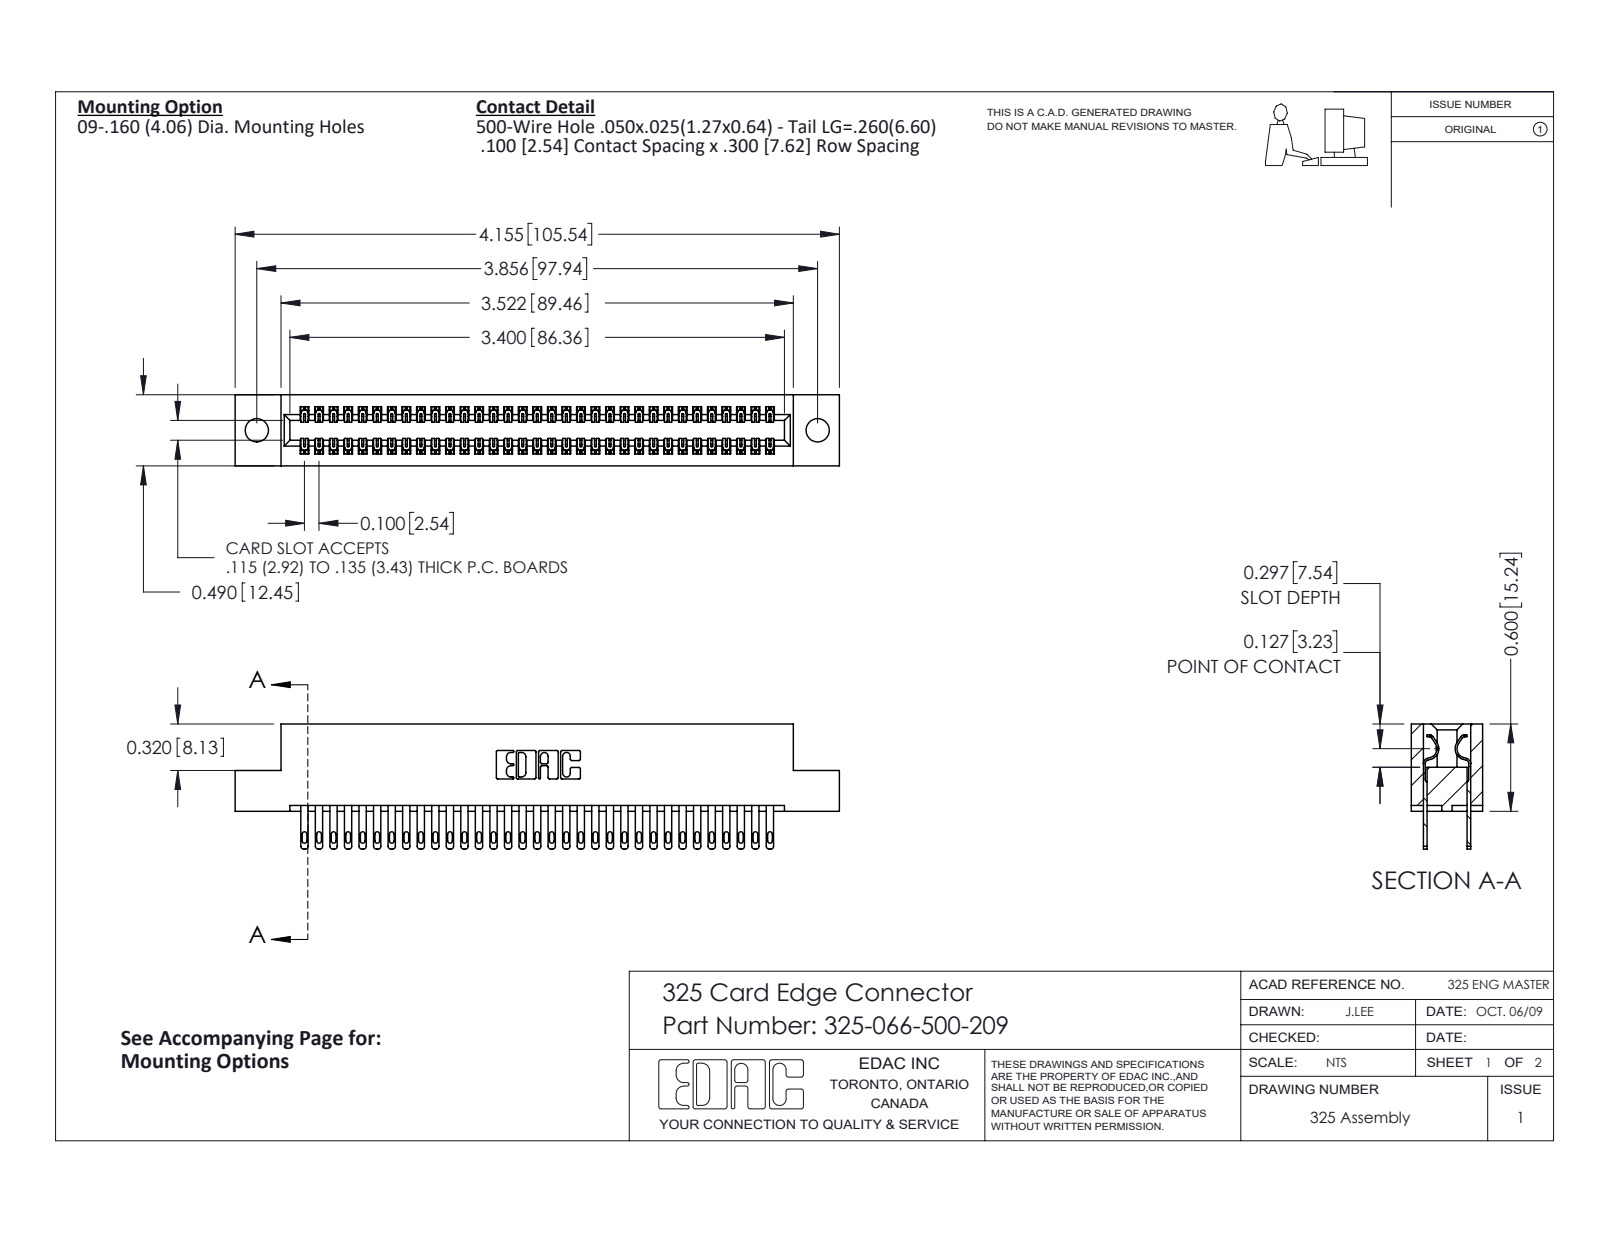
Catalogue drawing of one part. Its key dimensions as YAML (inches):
part_name: "325 Part_.160 TH; 325-066-500-209; 325-292-001_325-293-100"
step_written_by: "SolidWorks 2016 (CONFIG_CONTROL_DESIGN)"
units: inches
bodies: {solids: 67, faces: 3282, planar: 2050, cylindrical: 1232, other: 0}
overall_size: [4.155, 0.86, 0.49]
volume: 0.825
surface_area: 25.97
round_holes:
  - {diameter: 0.16, count: 2}
partial_cylinders:
  - {radius: 0.006, count: 99}
  - {radius: 0.016, count: 66}
  - {radius: 0.02, count: 66}
  - {radius: 0.01, count: 22}
  - {radius: 0.007, count: 6}
  - {radius: 0.031, count: 6}
  - {radius: 0.026, count: 3}
  - {radius: 0.014, count: 2}
face_to_face_distances: [0.083, 0.407, 0.3, 0.107, 0.383, 0.025, 0.49, 0.325, 0.275, 0.56]
hole_center_spacings: [3.856]
